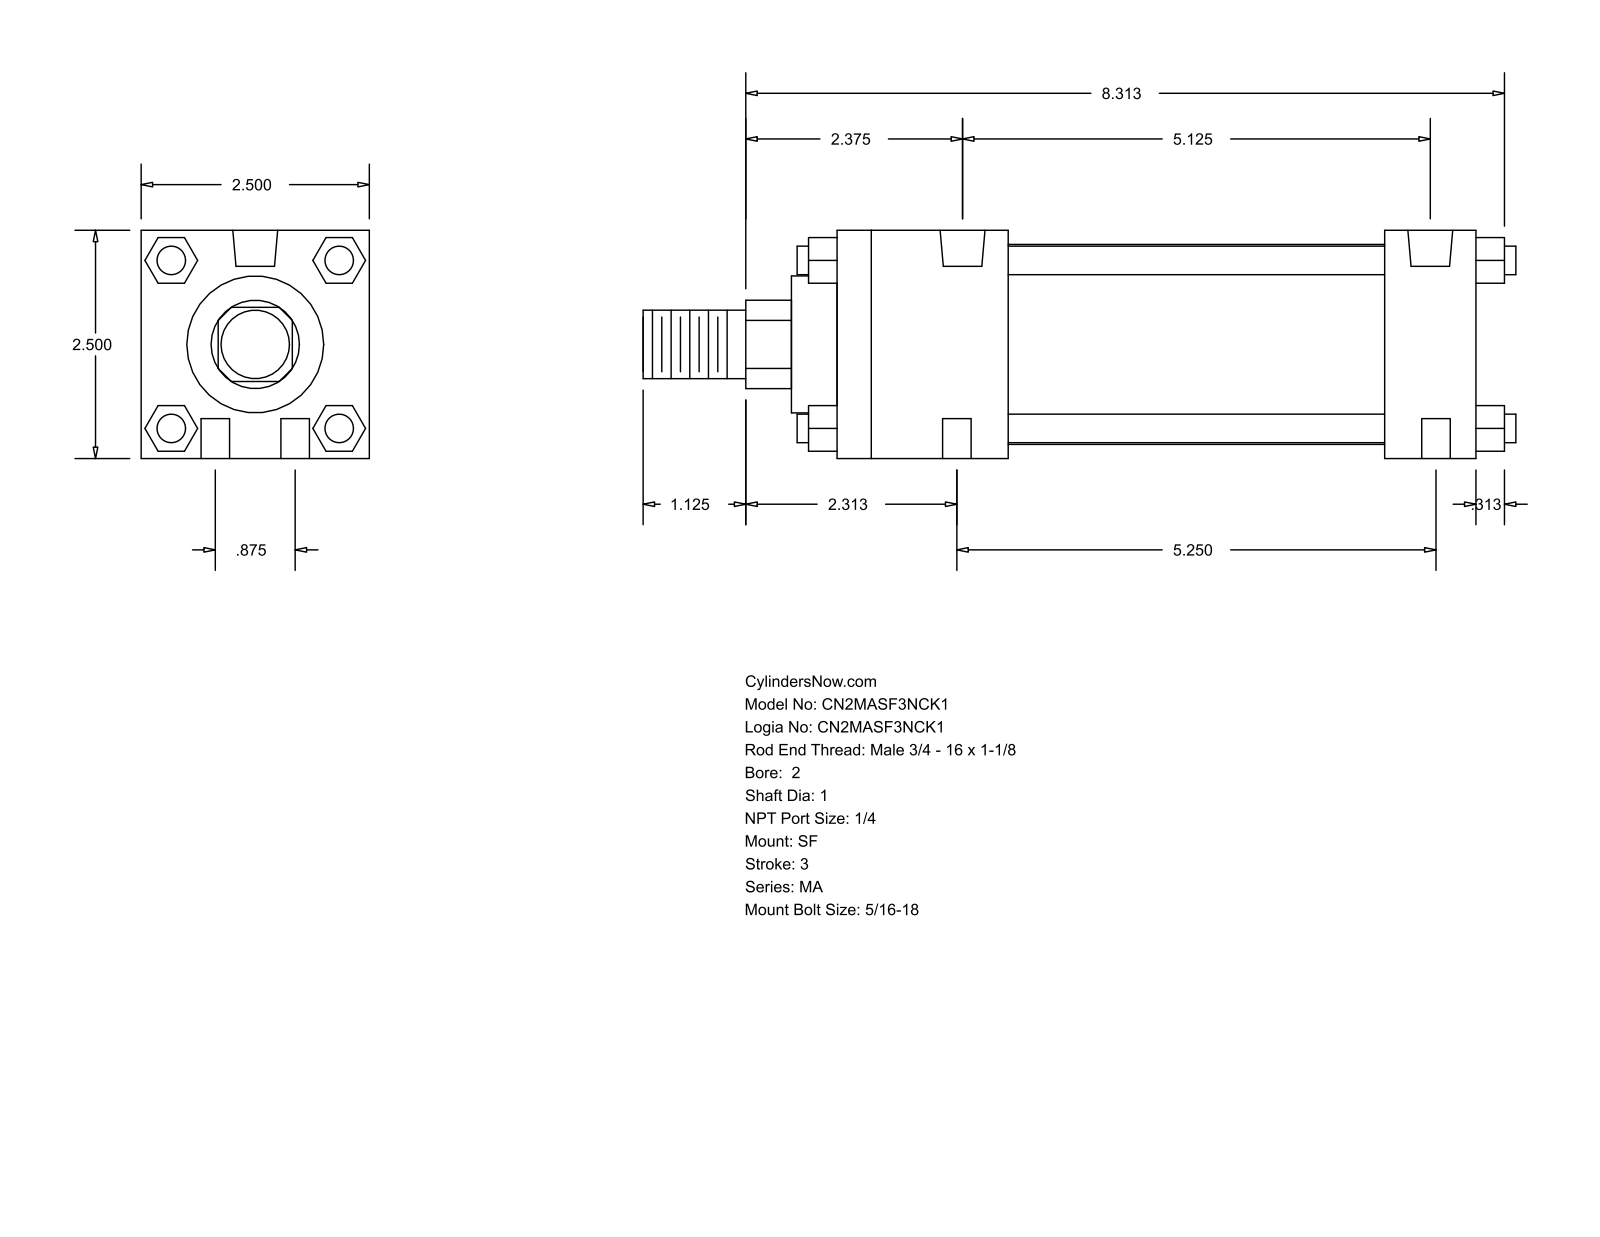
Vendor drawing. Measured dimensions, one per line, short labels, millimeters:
name: MA_SF__0200_1
written by: GSSL Pune (CONFIG_CONTROL_DESIGN)
unit: mm
bodies: 0 solids, 124 faces (94 planar, 30 cylindrical, 0 other)
size: 242.89 × 63.5 × 63.5
holes: 6× ⌀7.94, 2× ⌀12.49
bosses: 4× ⌀7.94, 1× ⌀55.63, 1× ⌀38.1, 1× ⌀25.4, 1× ⌀19.05
rounds: 1× R12.29
face distances: 63.5, 177.8, 12.7, 25.4, 152.4, 47.63, 104.77, 130.17, 23.37, 40.47
hole spacings: 11.22, 132.23, 22.22, 130.17, 133.35, 135.19
